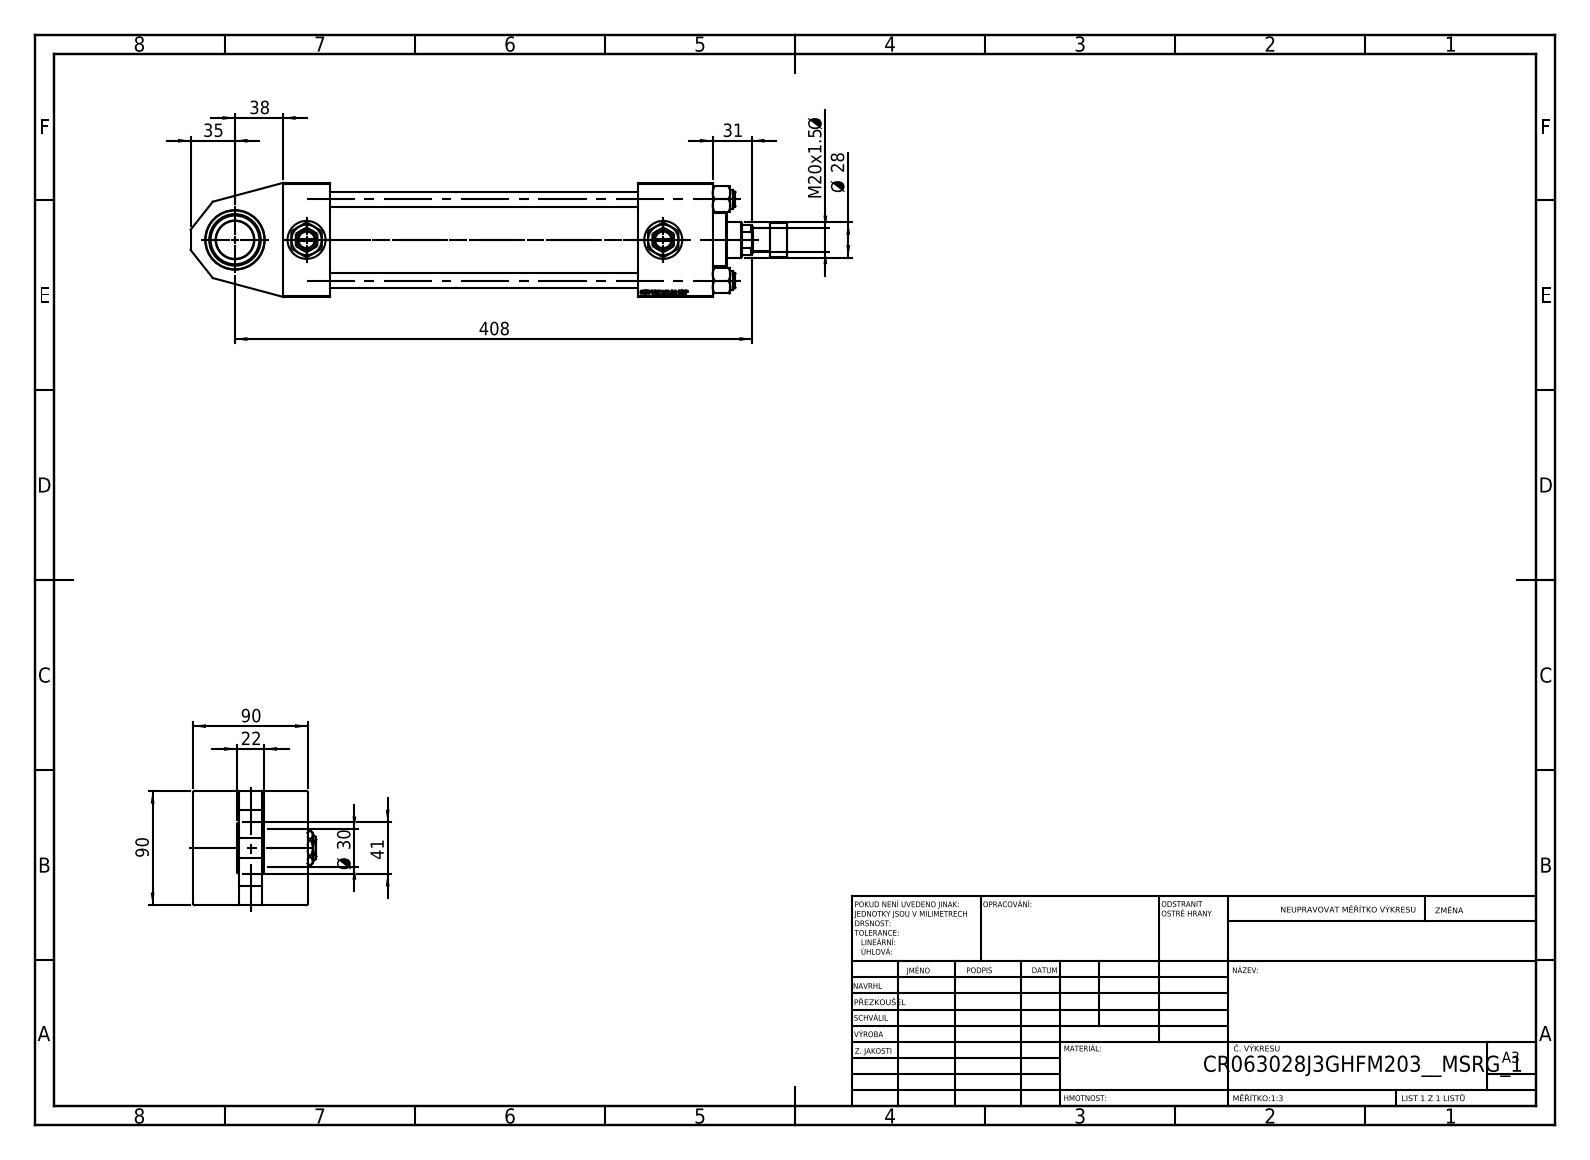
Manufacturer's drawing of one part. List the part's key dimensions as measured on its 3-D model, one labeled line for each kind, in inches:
Part name (STEP PRODUCT): V215CR_J_VNITRNI_KROUZEK; V215CR_VCP_J; V215_VC_A; V215CR_TYCINKA_J (+4 more)
STEP written by: SolidWorks 2019 (CONFIG_CONTROL_DESIGN)
Units: inches
Bodies: 15 solids, 1260 faces (568 planar, 104 cylindrical, 588 other)
Overall size (bounding box): 18.543 × 3.819 × 3.543
Volume: 82.2 in³ · Surface area: 508.8 in²
Round holes (diameter × count): ⌀0.472 ×4, ⌀1.181 ×3, ⌀0.098 ×2, ⌀0.276 ×2, ⌀0.825 ×2, ⌀0.728 ×1, ⌀1.102 ×1, ⌀1.22 ×1, ⌀1.85 ×1, ⌀1.969 ×1, ⌀2.362 ×1, ⌀2.48 ×1
Round bosses / shafts (diameter × count): ⌀0.591 ×4, ⌀2.717 ×1, ⌀1.654 ×1, ⌀1.063 ×1, ⌀0.709 ×1
Main face-to-face distances: 3.543, 2.126, 1.417, 11.89, 1.457, 13.346, 2.323, 11.024, 9.567, 0.709
Hole centre spacings: 1.275, 1.79, 2.531, 2.694, 1.112, 2.224, 3.58, 11.083
